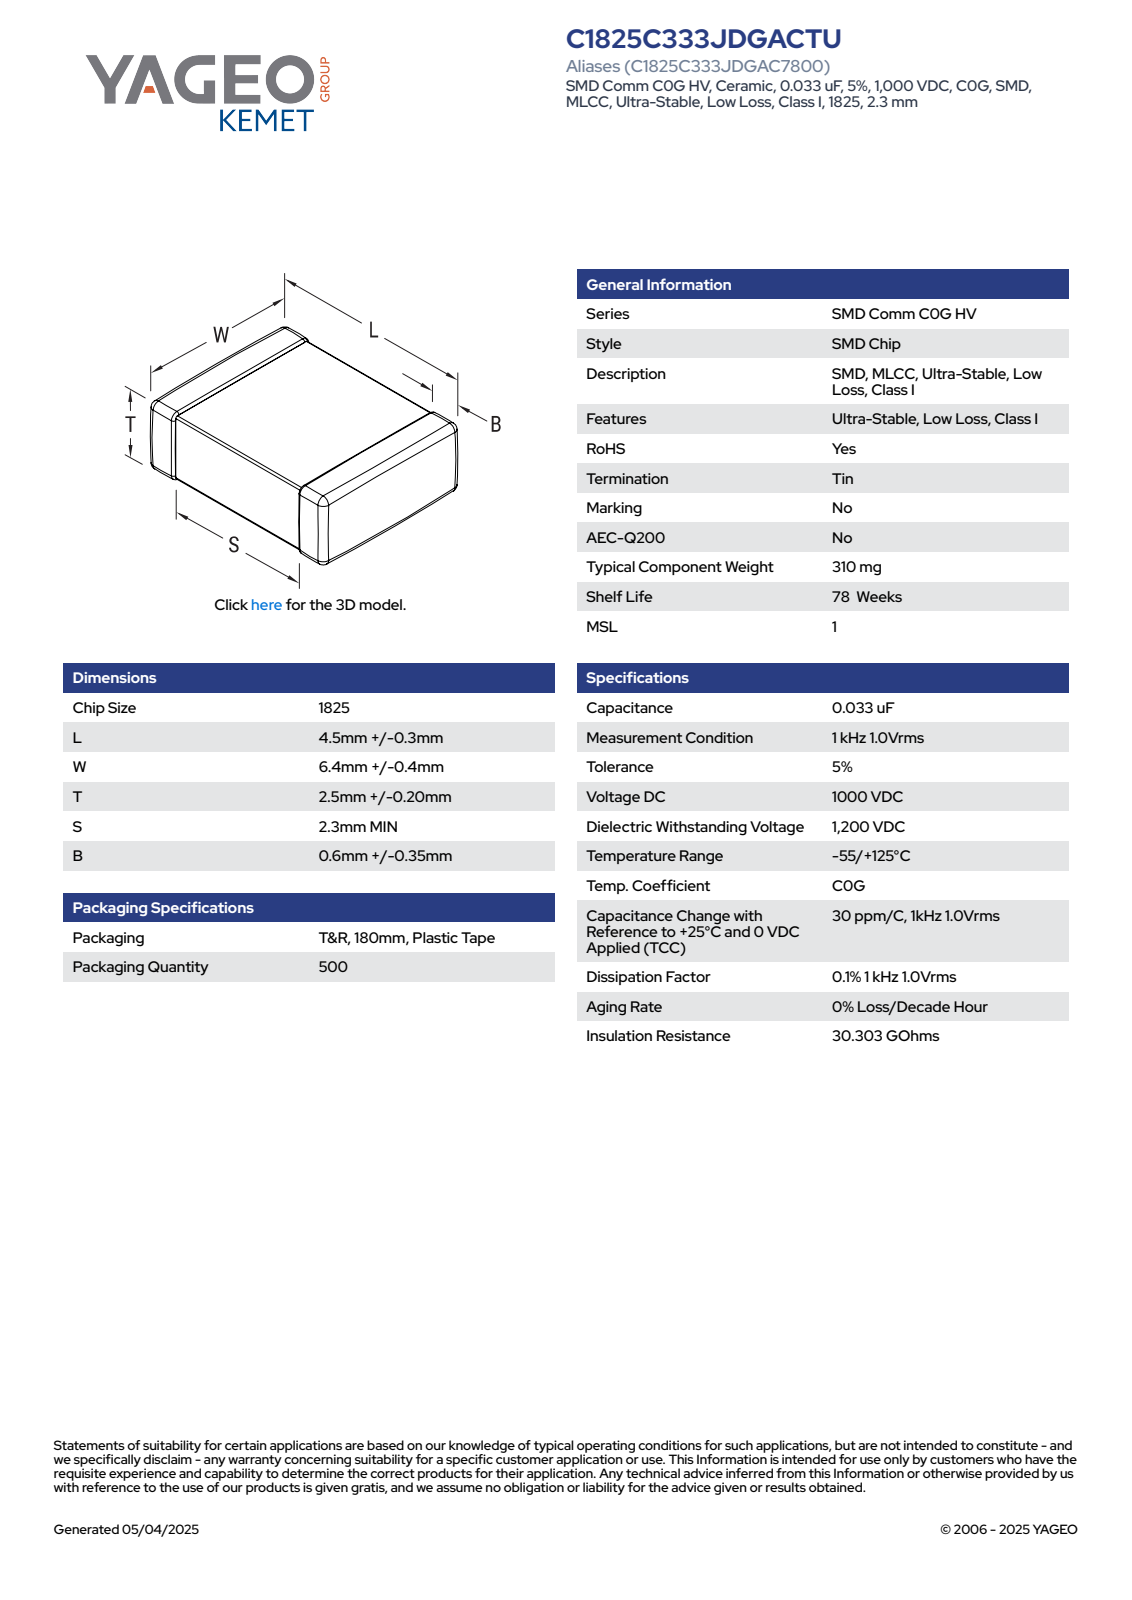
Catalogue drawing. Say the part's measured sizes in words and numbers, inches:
The part is named "CCS_CCSTD_1825_L4.8W6.8T2.7B0.6". Its 3-D file was written by "SolidWorks 2021 (AUTOMOTIVE_DESIGN)". It is 4 solids with 129 faces: 71 planar, 42 cylindrical and 16 other. Overall it measures 0.268 by 0.189 by 0.106 inches. Its volume is 0.005 cubic inches and its surface area 0.202 square inches. Partial cylindrical surfaces (rounded edges, fillets, slot ends): 24 of radius 0.006. The main face-to-face distances are 0.095, 0.101, 0.189, 0.106, 0.262, 0.257, 0.268, 0.063, 0.126, 0.102.
